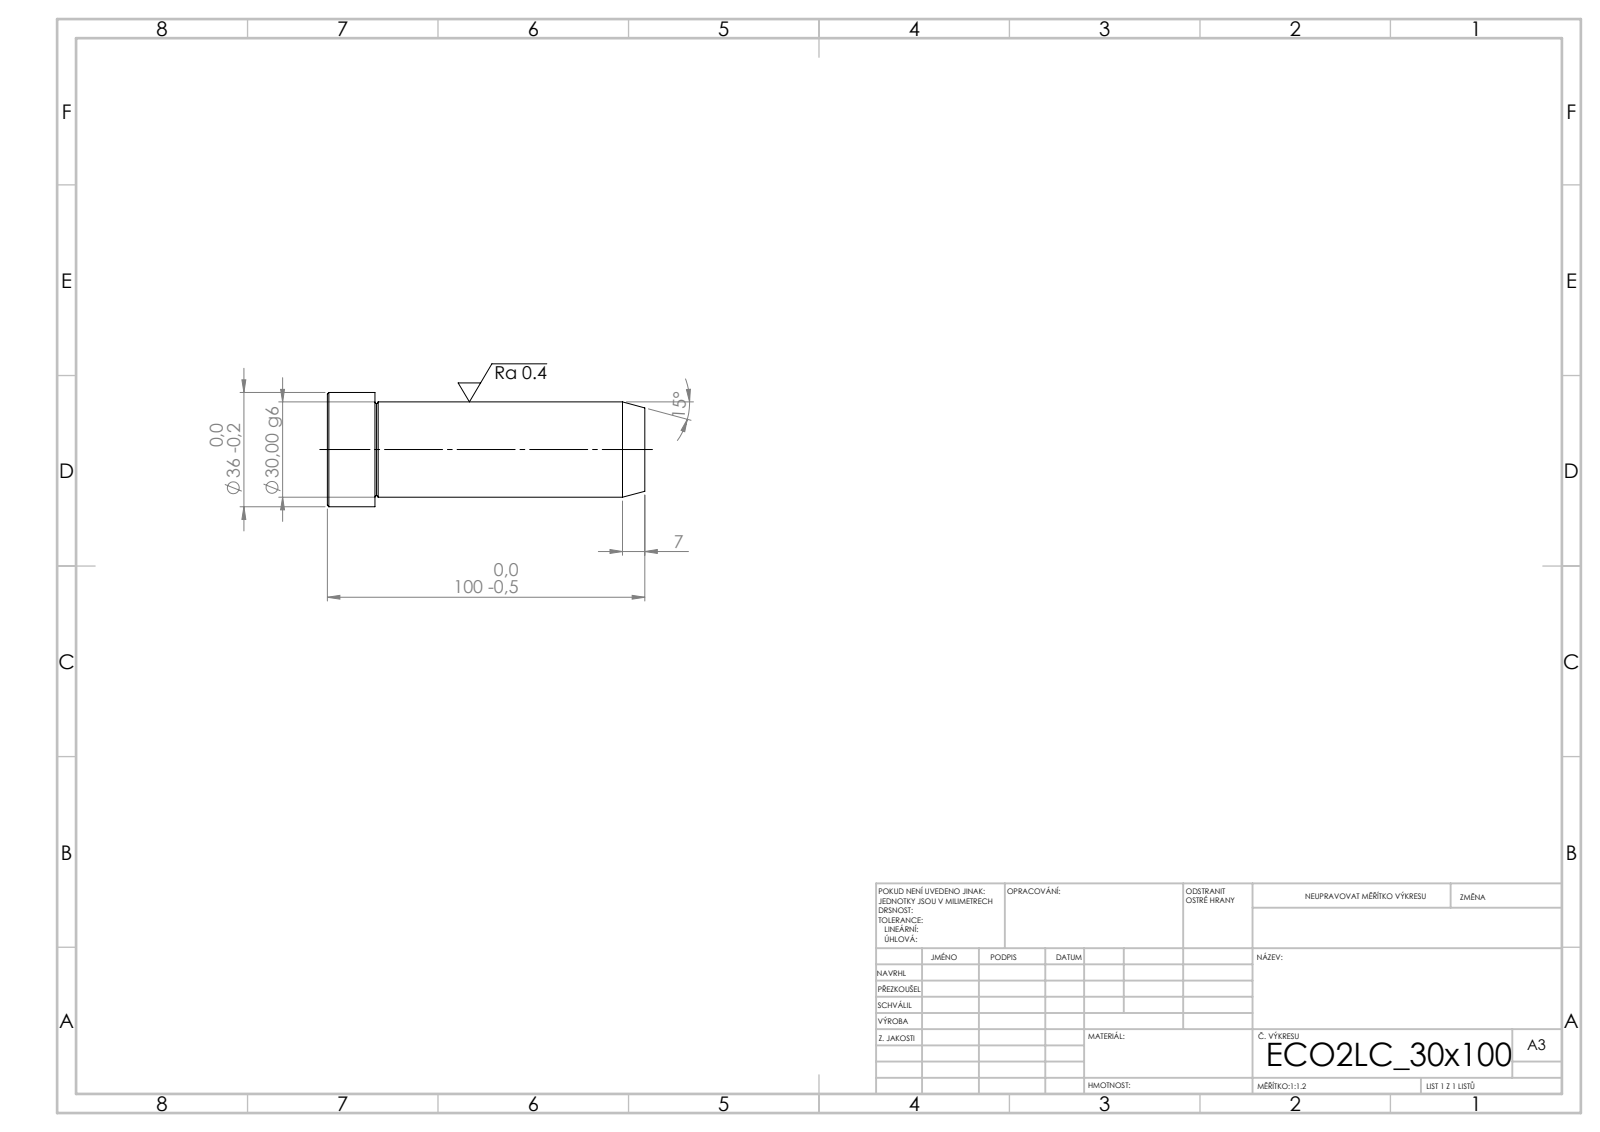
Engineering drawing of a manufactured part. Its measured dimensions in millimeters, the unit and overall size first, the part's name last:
Units: millimetres
Overall size (bounding box): 100 × 36 × 36
Round bosses / shafts (diameter × count): ⌀36 ×1, ⌀30 ×1
Main face-to-face distances: 100, 85, 15
Volume: 74 708 mm³ · Surface area: 11 575 mm²
Bodies: 1 solid, 15 faces (3 planar, 4 cylindrical, 8 other)
STEP written by: SolidWorks 2019 (CONFIG_CONTROL_DESIGN)
